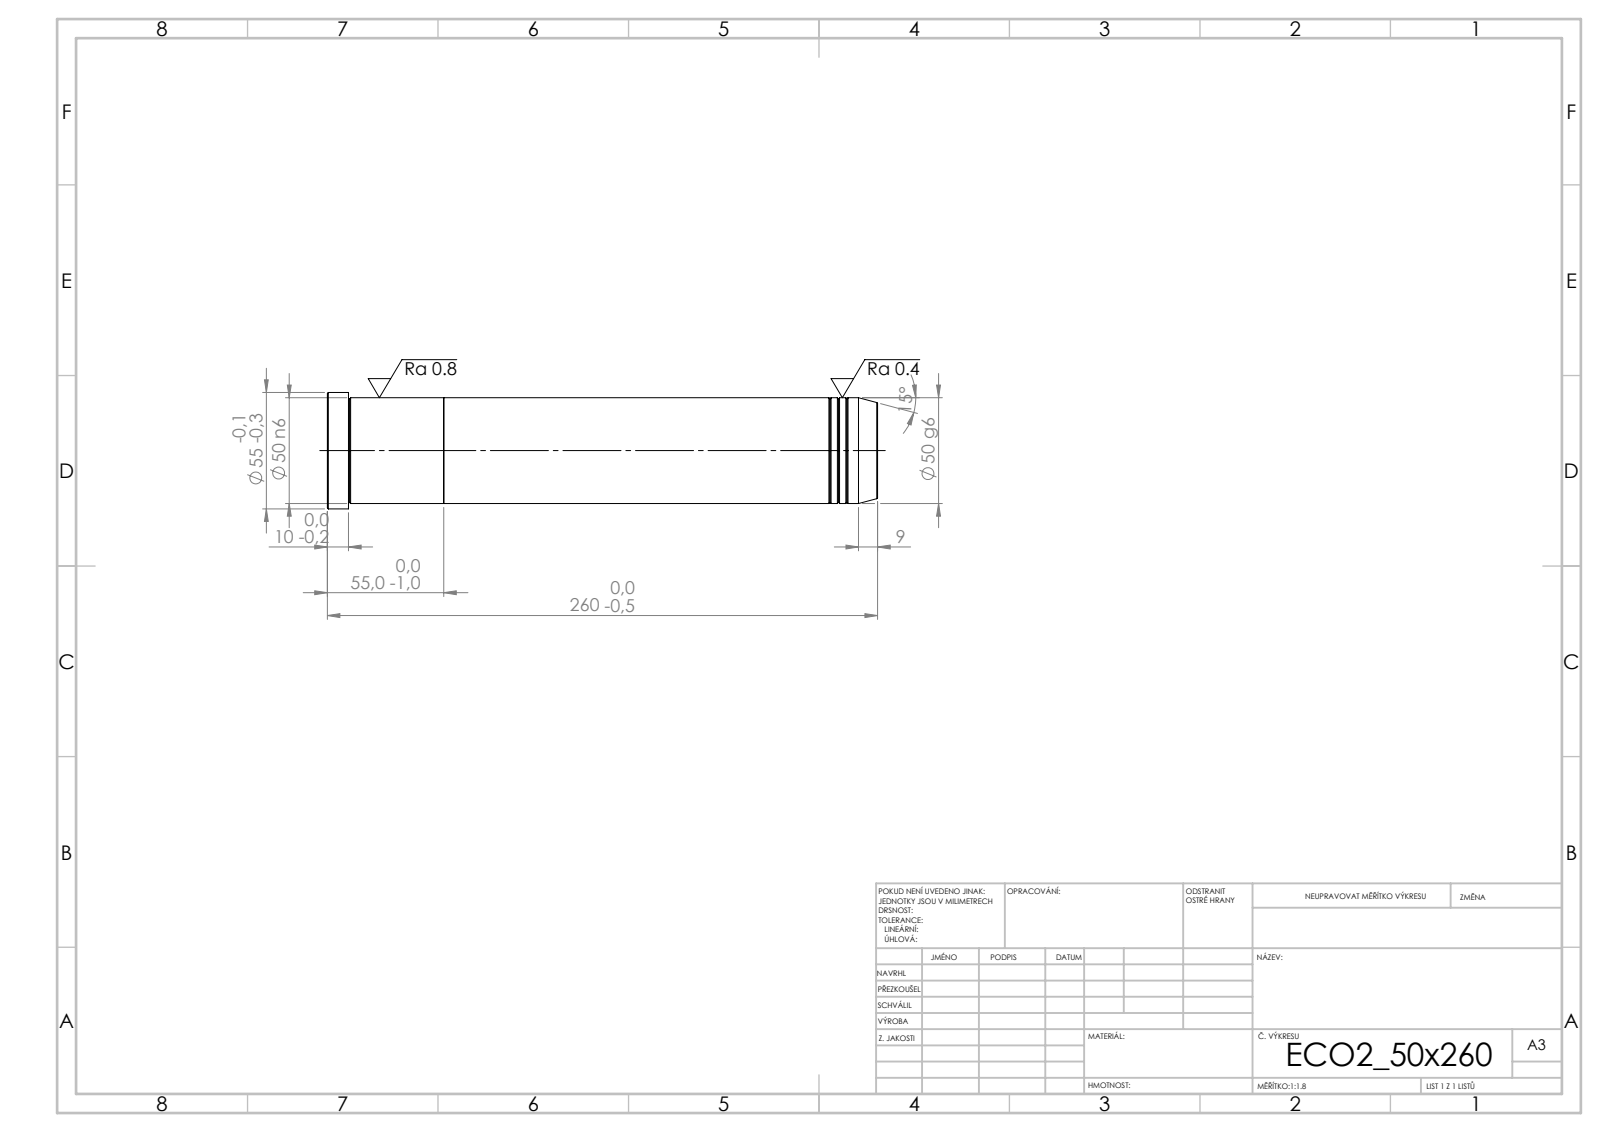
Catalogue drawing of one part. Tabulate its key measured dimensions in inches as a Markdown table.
| quantity | value |
| --- | --- |
| STEP written by | SolidWorks 2019 (CONFIG_CONTROL_DESIGN) |
| units | inches |
| bodies | 2 solids, 39 faces (5 planar, 12 cylindrical, 22 other) |
| overall size | 10.236 × 2.165 × 2.165 |
| volume | 31.29 in³ |
| surface area | 76.84 in² |
| round bosses / shafts (diameter × count) | 2.165 × 1, 1.969 × 1 |
| main face-to-face distances | 2.165, 8.071, 10.236, 9.843, 1.772, 0.394 |
